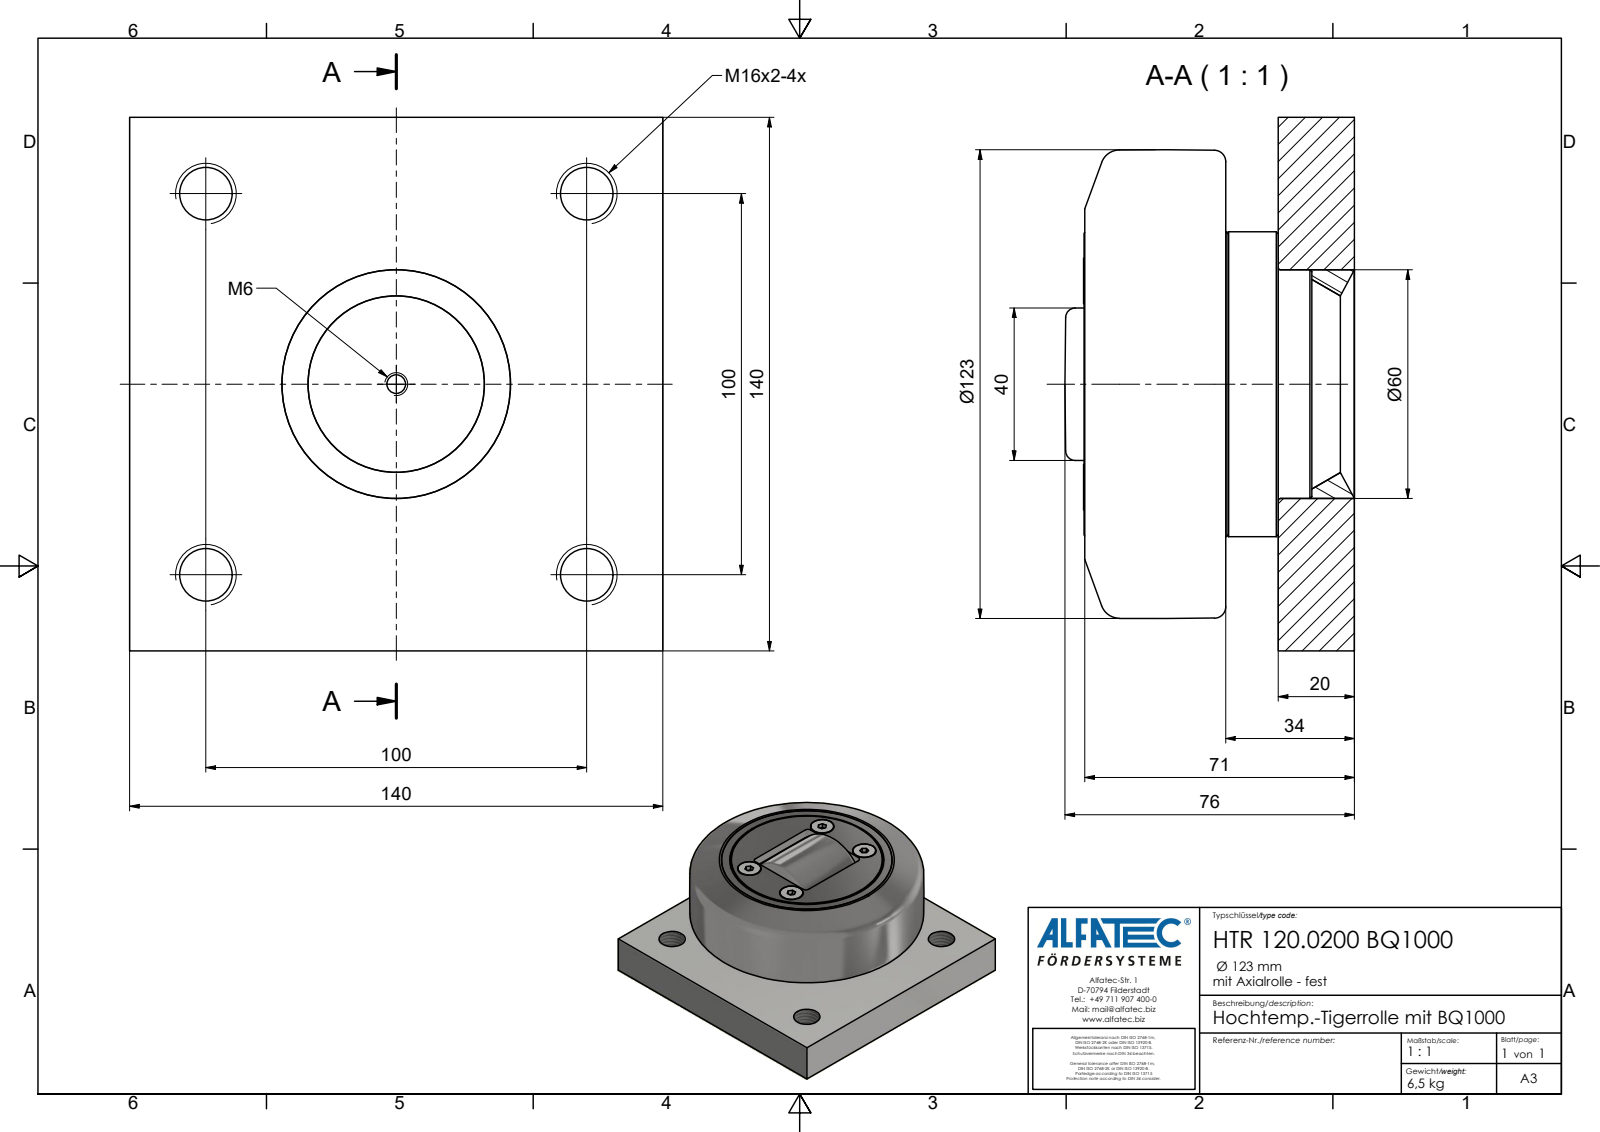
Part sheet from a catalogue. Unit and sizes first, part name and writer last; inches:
Units: inches
Overall size (bounding box): 5.512 × 5.512 × 2.992
Round holes (diameter × count): ⌀0.118 ×4, ⌀0.545 ×4, ⌀0.194 ×1, ⌀0.878 ×1, ⌀1.154 ×1, ⌀1.319 ×1, ⌀2.795 ×1, ⌀3.189 ×1, ⌀3.425 ×1, ⌀3.524 ×1, ⌀3.74 ×1
Round bosses / shafts (diameter × count): ⌀0.472 ×4, ⌀3.327 ×1, ⌀3.15 ×1, ⌀3.142 ×1, ⌀3.11 ×1, ⌀2.736 ×1
Partial cylindrical surfaces — rounded edges, fillets, slot ends (radius × count): R0.079 ×8, R0.059 ×2, R0.965 ×1
Main face-to-face distances: 0.787, 5.512, 1.331, 0.543, 0.256, 2.795, 2.008, 1.465, 1.201, 1.209
Hole centre spacings: 2.784, 3.937, 5.568
Volume: 47.49 in³ · Surface area: 202.4 in²
Bodies: 3 solids, 143 faces (68 planar, 48 cylindrical, 27 other)
Part name (STEP PRODUCT): HTR 120.0200 BQ1000_Kontur
STEP written by: Autodesk Inventor 2020 (AUTOMOTIVE_DESIGN)
